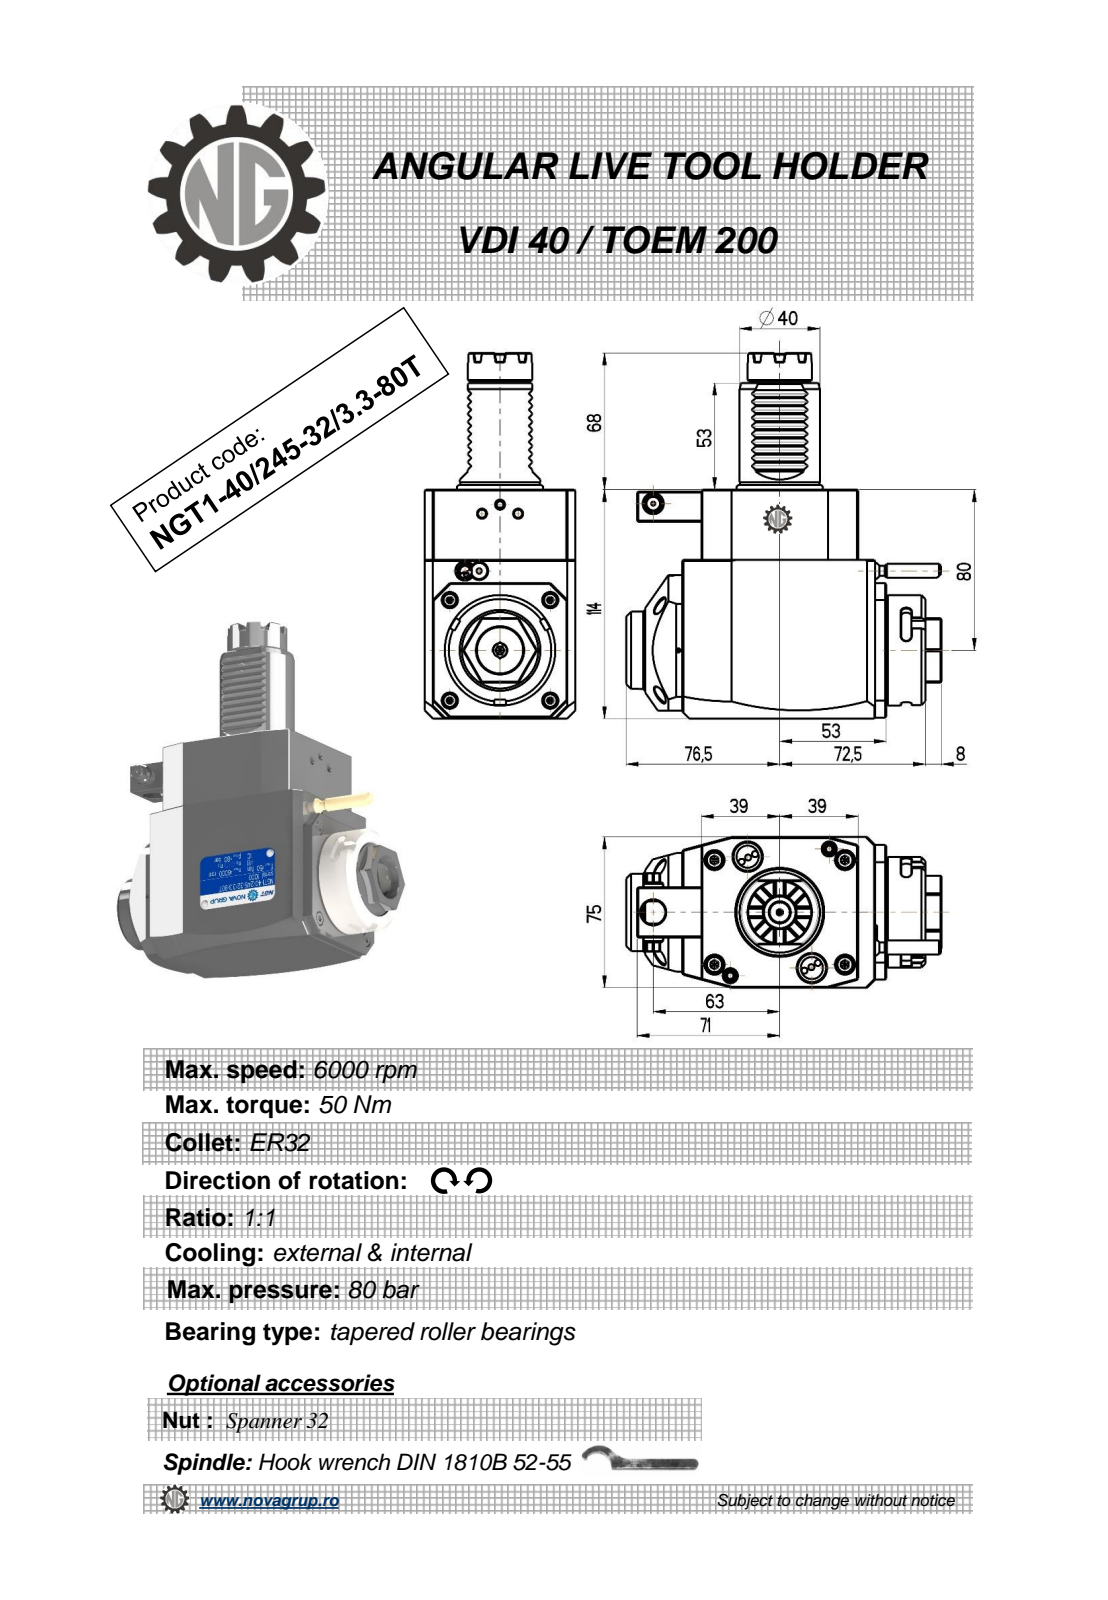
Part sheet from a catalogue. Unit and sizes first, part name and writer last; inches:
Units: inches
Overall size (bounding box): 7.165 × 6.181 × 2.953
Round holes (diameter × count): ⌀0.079 ×1, ⌀0.098 ×1, ⌀0.118 ×1, ⌀0.177 ×1, ⌀0.374 ×1, ⌀0.472 ×1, ⌀0.906 ×1
Round bosses / shafts (diameter × count): ⌀0.315 ×2, ⌀2.165 ×1, ⌀1.89 ×1, ⌀1.575 ×1, ⌀1.516 ×1, ⌀1.26 ×1, ⌀0.677 ×1, ⌀0.394 ×1
Partial cylindrical surfaces — rounded edges, fillets, slot ends (radius × count): R0.012 ×20, R0.098 ×6, R7.087 ×2, R0.152 ×1, R0.167 ×1, R0.965 ×1, R1.476 ×1
Main face-to-face distances: 2.953, 4.488, 0.551, 3.071, 3.622, 0.984, 4.39, 1.319, 0.768, 1.378
Hole centre spacings: 1.47, 1.701, 2.854
Volume: 59.12 in³ · Surface area: 114.8 in²
Bodies: 1 solid, 478 faces (263 planar, 95 cylindrical, 120 other)
Part name (STEP PRODUCT): NGT1_40_245_32_3_3_80T
STEP written by: PRO/ENGINEER BY PARAMETRIC TECHNOLOGY CORPORATION, 2010280 (CONFIG_CONTROL_DESIGN)
